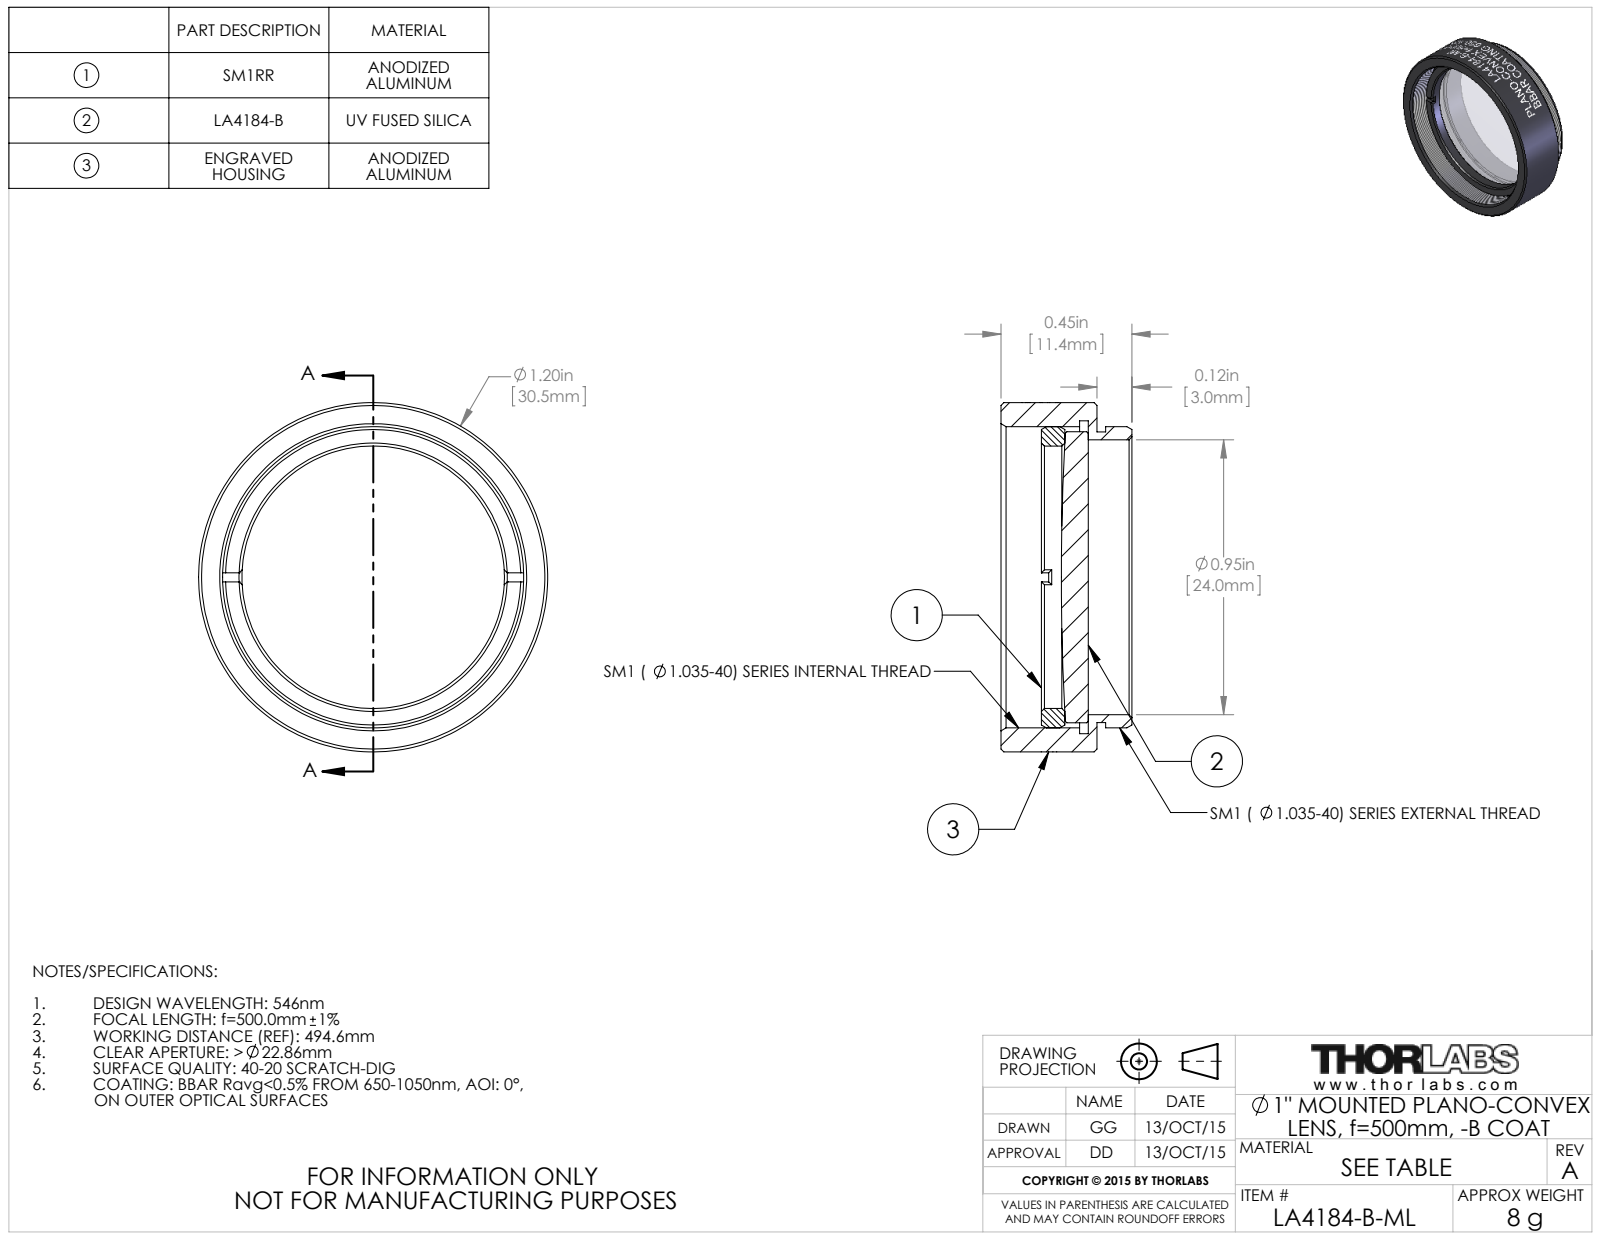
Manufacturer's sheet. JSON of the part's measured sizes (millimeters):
{"part_name": "TTN039201-E0W", "step_written_by": "SolidWorks 2014 (CONFIG_CONTROL_DESIGN)", "units": "millimeters", "bodies": {"solids": 3, "faces": 165, "planar": 20, "cylindrical": 117, "other": 28}, "overall_size": [30.48, 30.48, 11.43], "volume_mm3": 3182, "surface_area_mm2": 4300, "round_holes": [[22.91, 1], [24, 1], [27.31, 1]], "round_bosses_or_shafts": [[30.48, 1], [26.29, 1], [25.4, 1], [25.37, 1]], "face_to_face_distances": [0.76, 8.38, 7.62, 2.82, 2.06, 5.56, 4.85, 4.09, 2.03, 3.53]}
